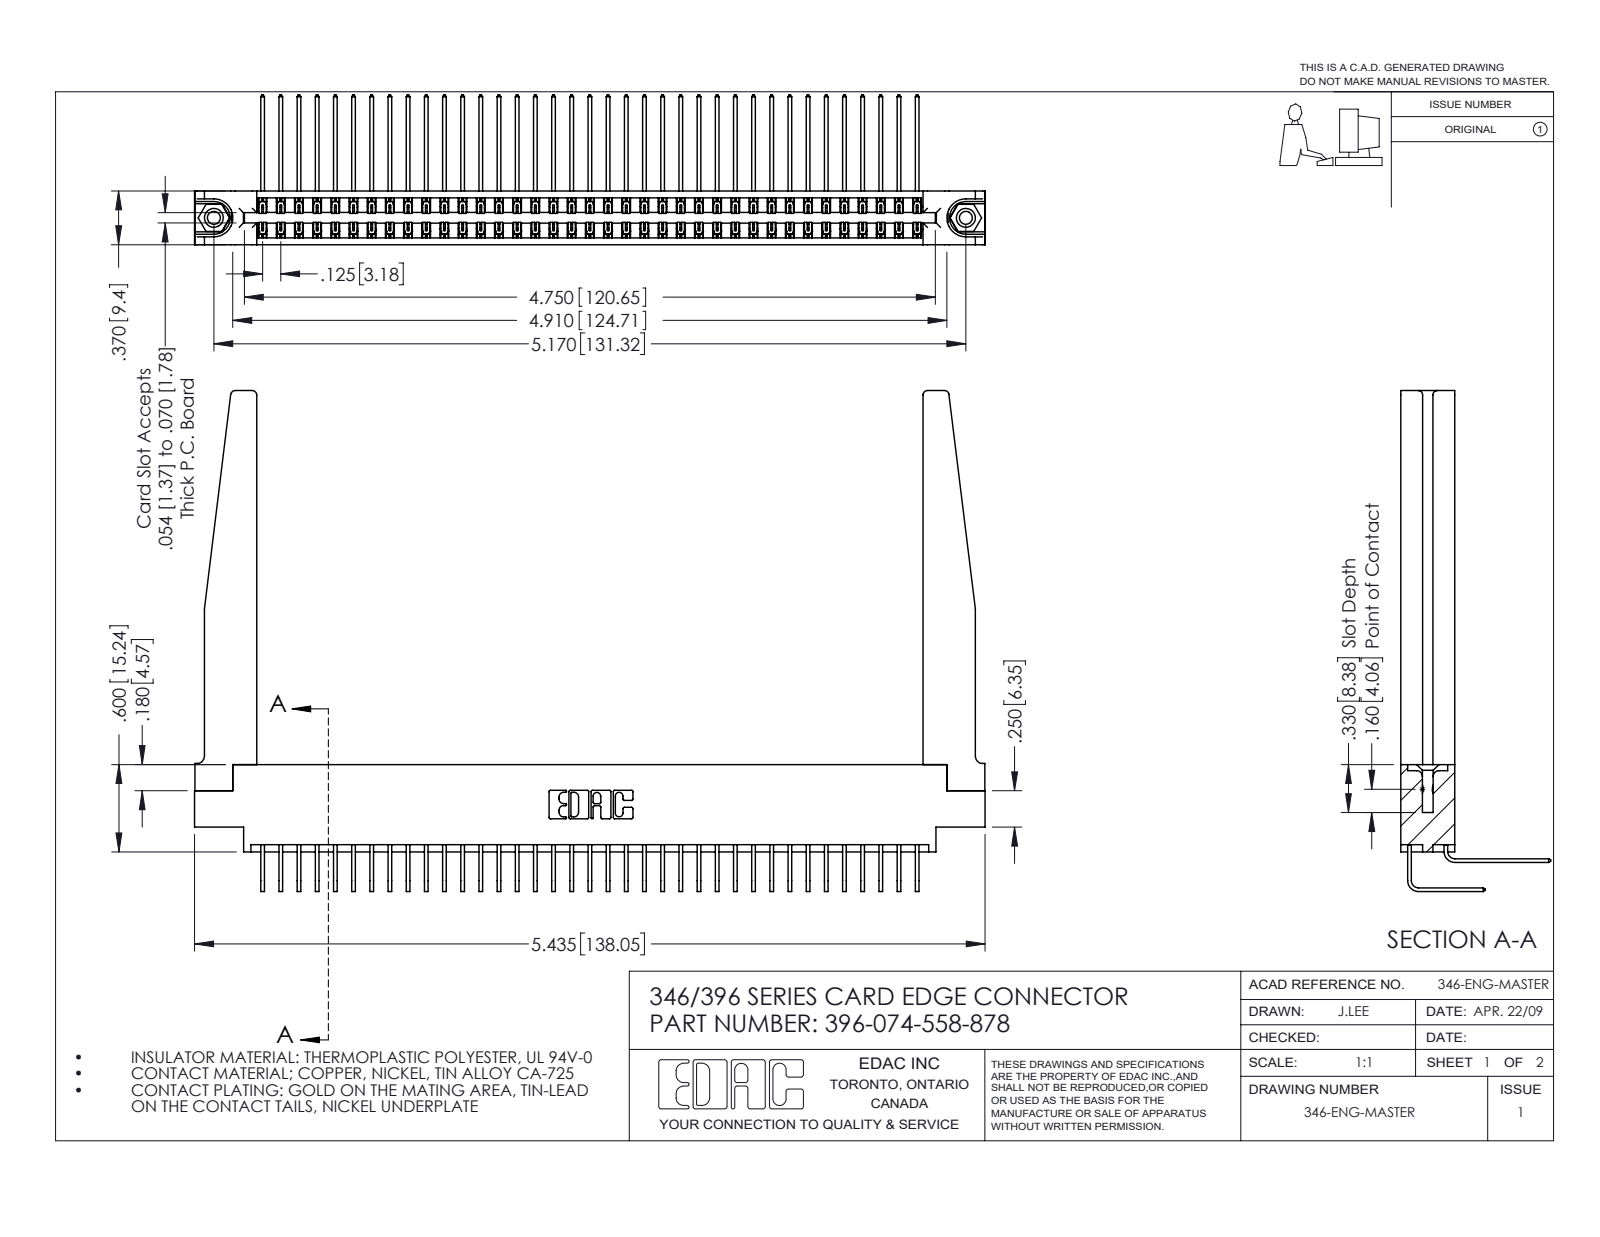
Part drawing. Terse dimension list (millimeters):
name: 396-074-558-878; 346-220-078_345-220-078; 345-250-001_345-250-001-102; 345-292-001_558 559 Tail - 1 (+2 more)
written by: SolidWorks 2016 (CONFIG_CONTROL_DESIGN)
unit: mm
bodies: 79 solids, 4356 faces (2960 planar, 1344 cylindrical, 52 other)
size: 138 × 87.5 × 26.2
volume: 20 600 mm³; area: 27 510 mm²
holes: 2× ⌀2.3, 2× ⌀3.2, 2× ⌀4, 1× ⌀1.6
bosses: 2× ⌀3.9
rounds: 111× R0.2, 22× R0.3, 8× R0.8, 6× R0.2, 6× R0.8, 4× R1.3, 3× R0.7, 2× R0.4
face distances: 9.4, 8.2, 1.2, 1.8, 0.6, 7.6, 6.4, 3.8, 3.8, 7
hole spacings: 6.2, 126, 131.3
